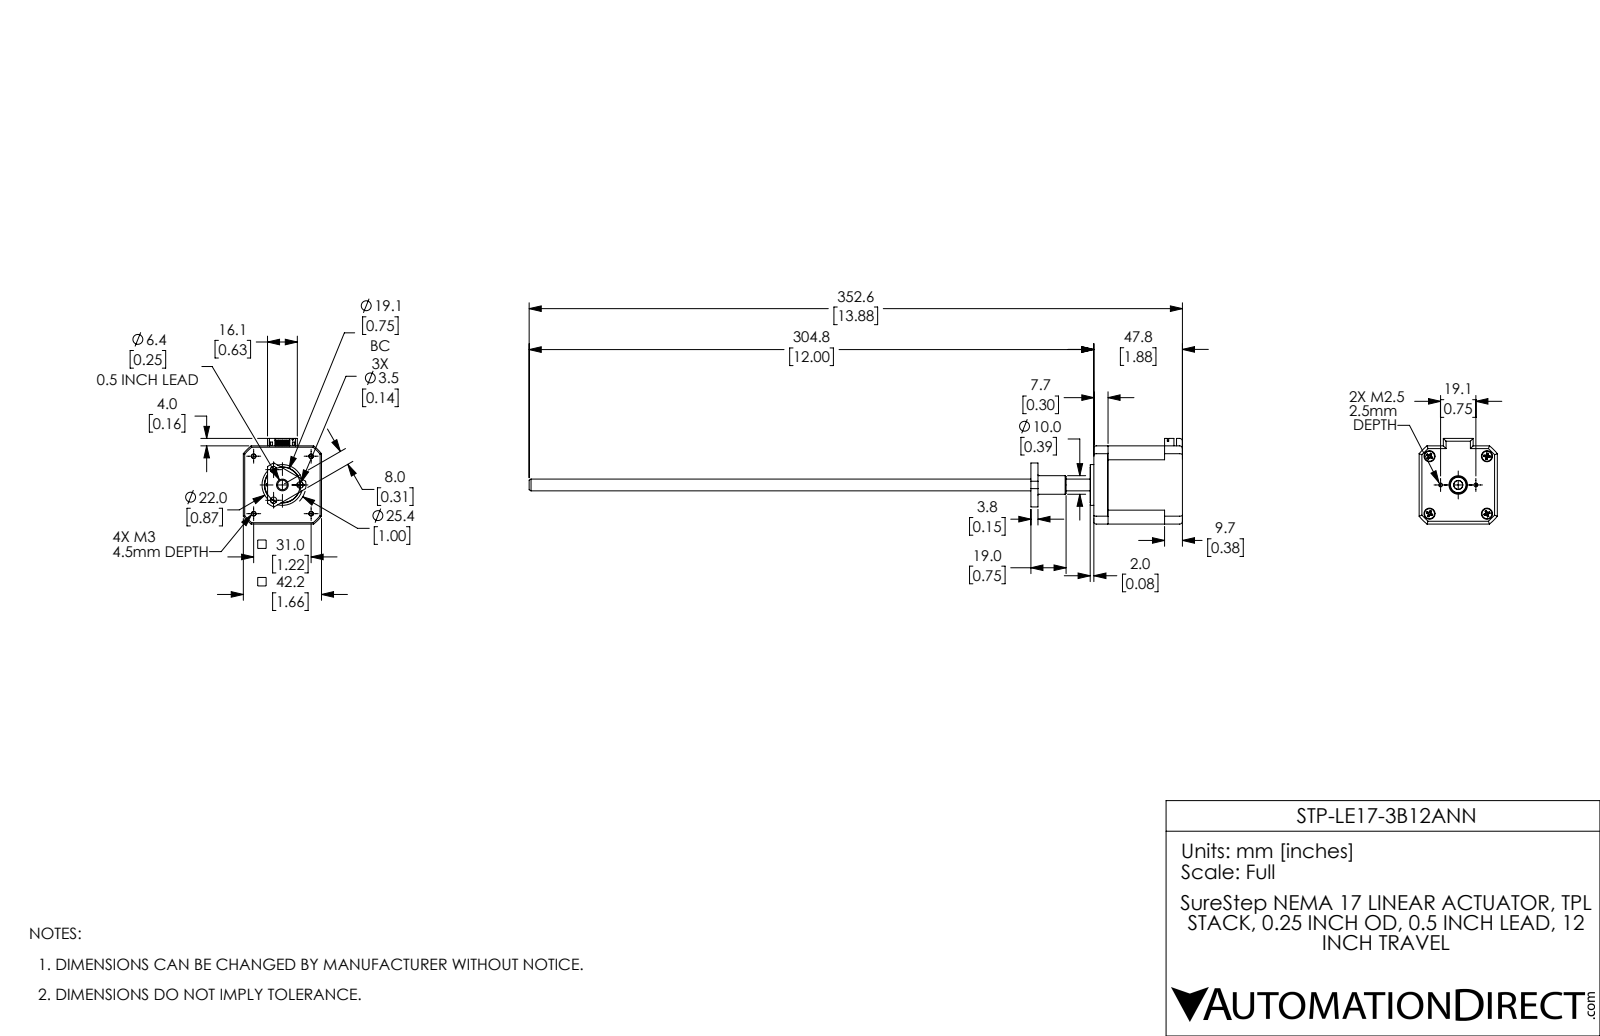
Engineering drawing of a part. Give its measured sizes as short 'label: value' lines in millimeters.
name: STP-LE17-3B12ANN; STP-LE17-3B12ANN_1; STP-LE17-3B12ANN_2
written by: SolidWorks 2017 (AUTOMOTIVE_DESIGN)
unit: mm
bodies: 5 solids, 730 faces (364 planar, 236 cylindrical, 130 other)
size: 352.6 × 46.2 × 42.2
volume: 82 923 mm³; area: 31 393 mm²
holes: 4× ⌀2.5, 4× ⌀3.8, 4× ⌀6, 3× ⌀3.5, 2× ⌀1.5, 2× ⌀2.05, 1× ⌀4.9, 1× ⌀13, 1× ⌀17, 1× ⌀19.46, 1× ⌀20
bosses: 4× ⌀5.4, 4× ⌀2.91, 1× ⌀27, 1× ⌀25.91, 1× ⌀22, 1× ⌀12, 1× ⌀10, 1× ⌀9
rounds: 12× R1, 11× R1.5, 2× R2.5, 1× R0.7, 1× R12.7, 1× R14.25, 1× R16, 1× R25.1
face distances: 42.2, 9.65, 47.8, 40.15, 38.15, 1.6, 30.5, 7.65, 45.3, 40.6
hole spacings: 16.61, 9.52, 21.92, 29.43, 31, 4.93, 8, 12.96
